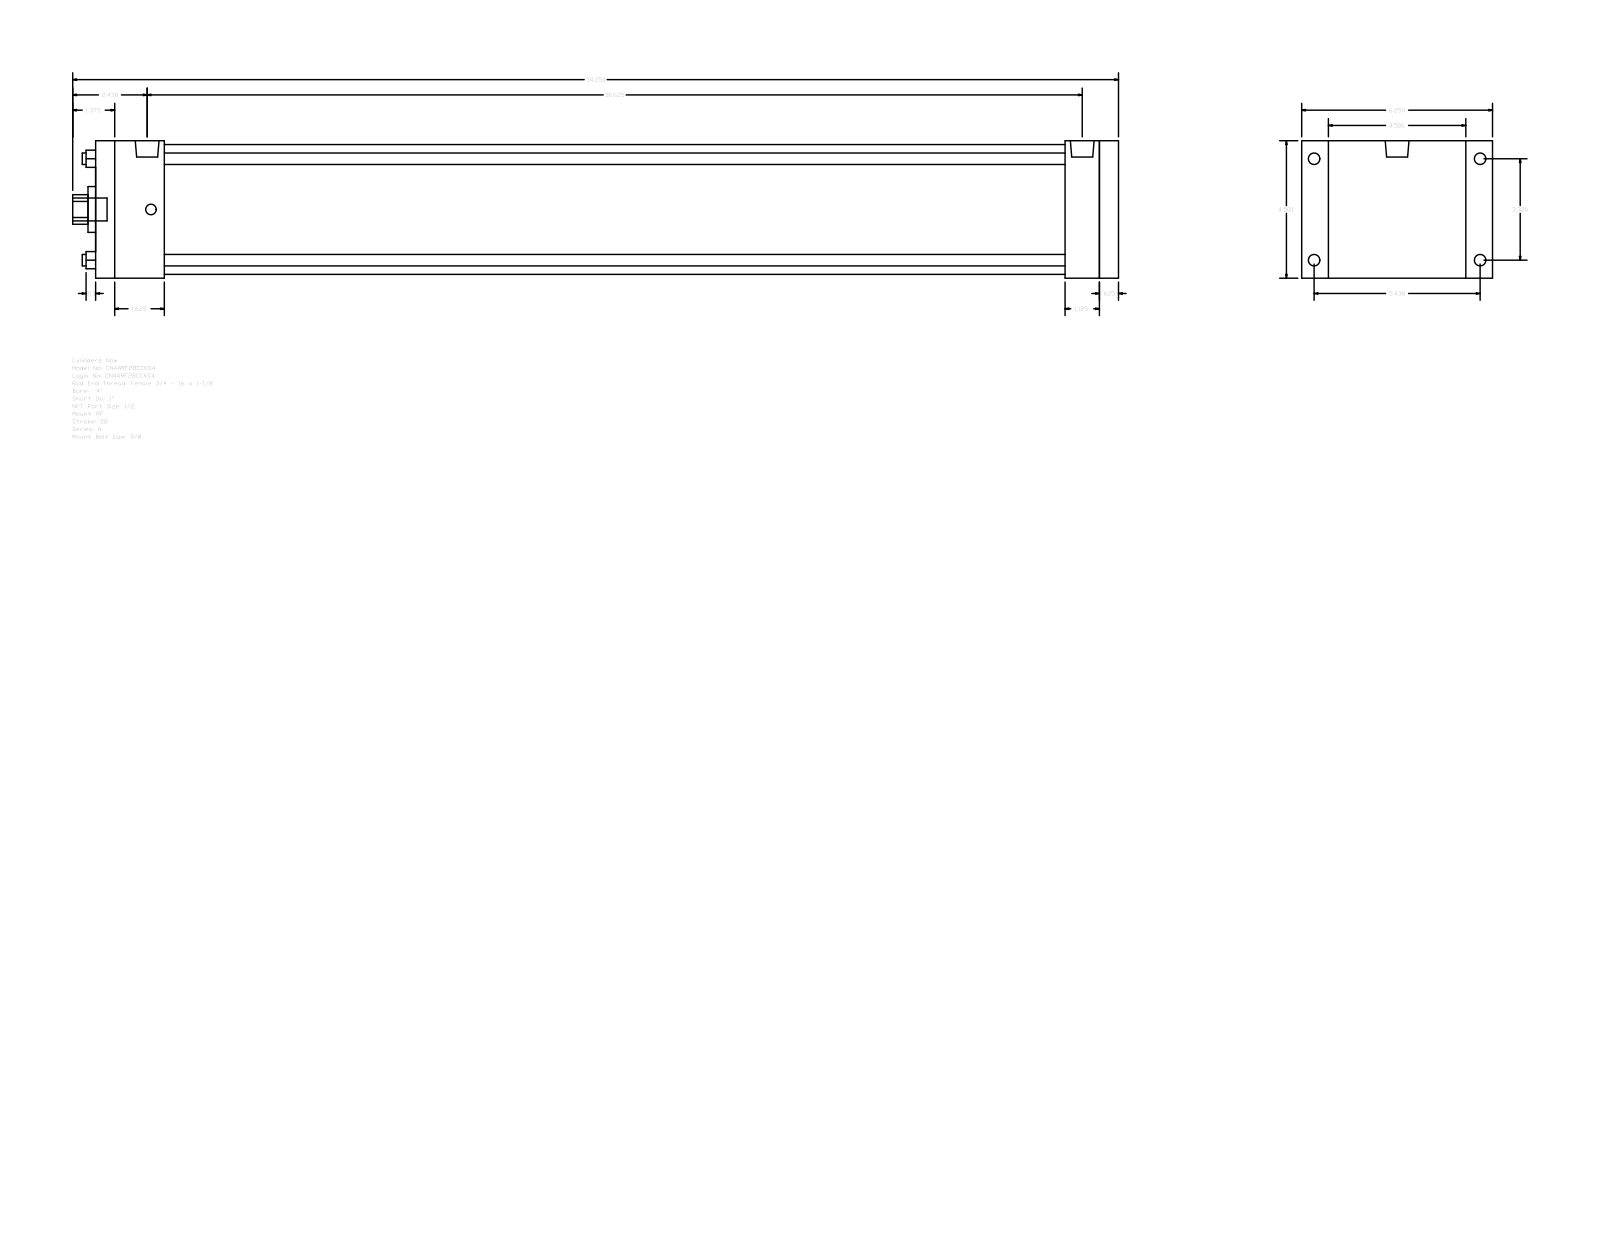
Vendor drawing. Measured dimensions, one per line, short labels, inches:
name: A_RF__0400_1
written by: GSSL Pune (CONFIG_CONTROL_DESIGN)
unit: in
bodies: 0 solids, 92 faces (64 planar, 28 cylindrical, 0 other)
size: 34.25 × 6.25 × 4.5
holes: 4× ⌀0.375, 1× ⌀1, 1× ⌀1.5, 1× ⌀4.25
bosses: 4× ⌀0.375, 4× ⌀0.344, 2× ⌀0.778, 1× ⌀0.75
rounds: 1× R0.484
face distances: 4.5, 33.5, 0.625, 32.875, 0.875, 5.375, 31.75, 1.125, 1.75, 2.25
hole spacings: 2.347, 3.32, 4.695
